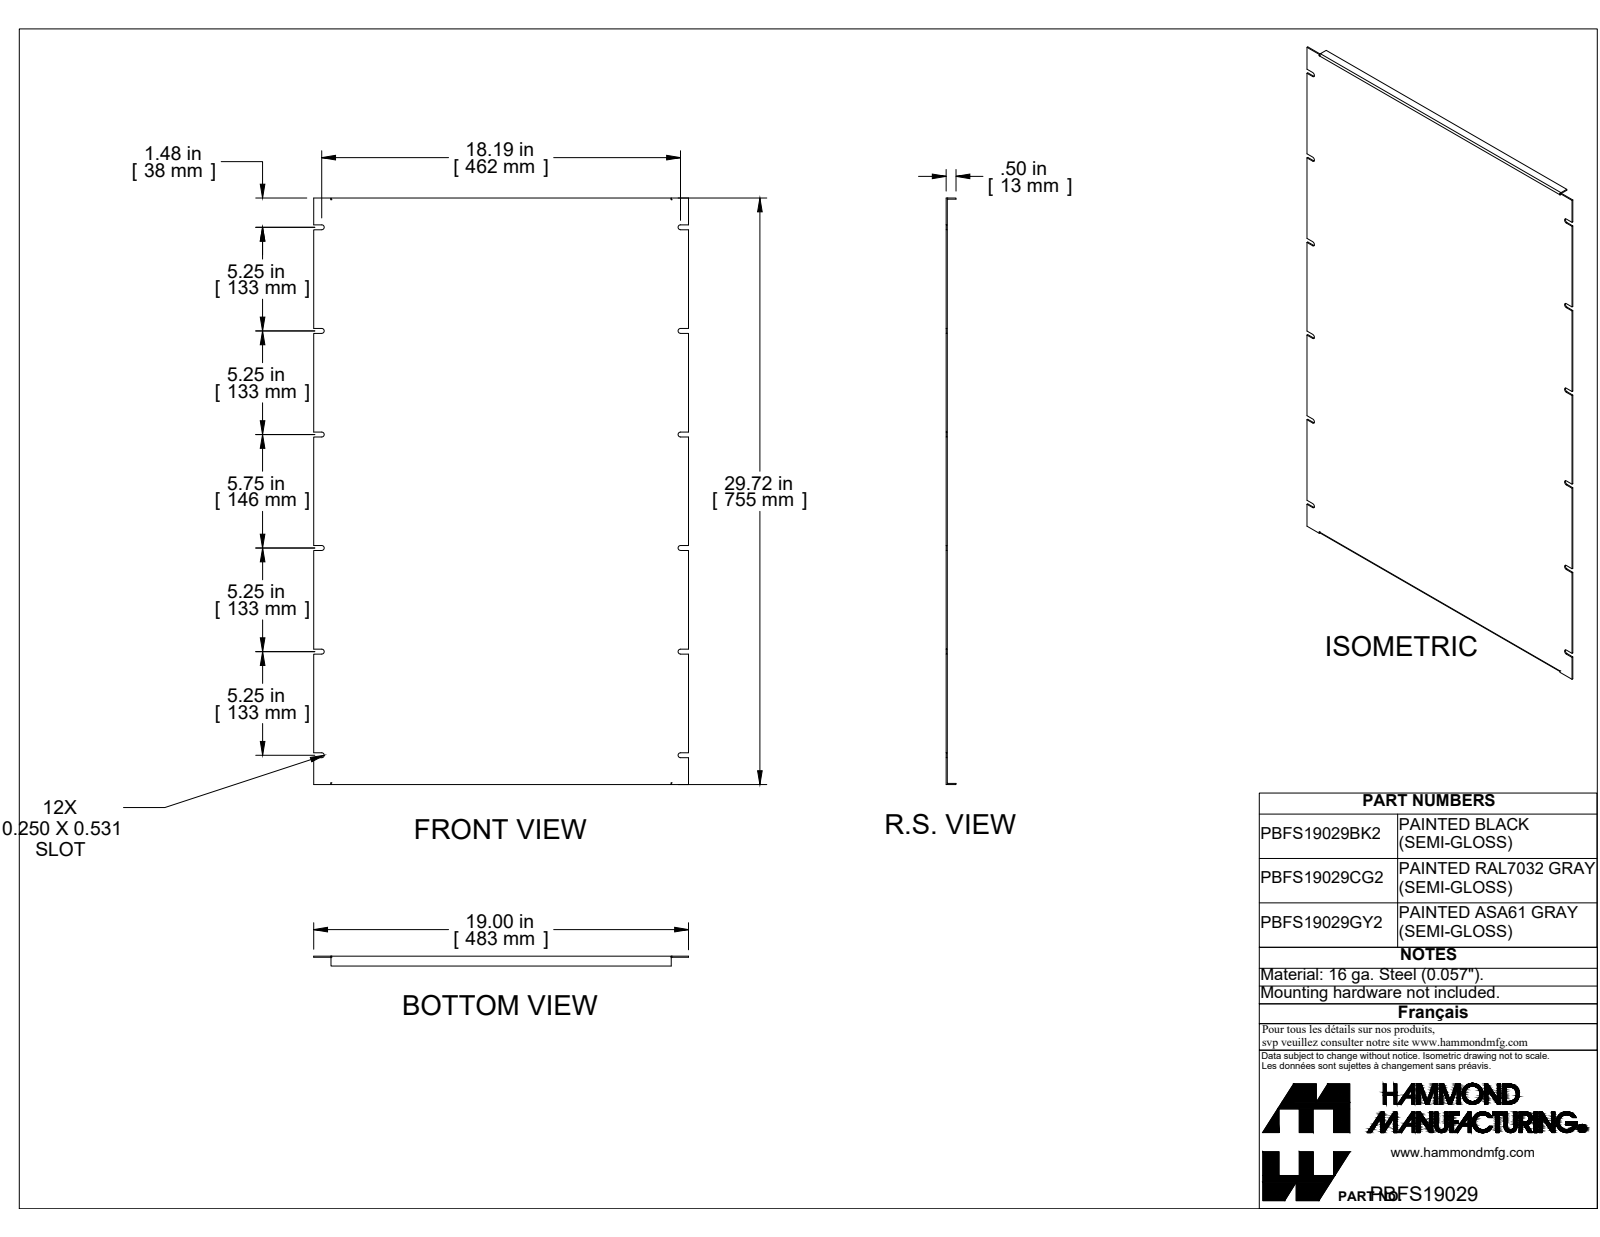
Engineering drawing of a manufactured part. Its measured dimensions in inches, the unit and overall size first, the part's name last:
Units: inches
Overall size (bounding box): 29.718 × 19 × 0.5
Partial cylindrical surfaces — rounded edges, fillets, slot ends (radius × count): R0.125 ×12, R0.029 ×2, R0.086 ×2
Main face-to-face distances: 0.057, 29.661, 29.718, 29.604, 0.5, 0.443, 19, 5.25, 0.25, 16.25
Volume: 32.92 in³ · Surface area: 1 161 in²
Bodies: 1 solid, 78 faces (62 planar, 16 cylindrical, 0 other)
Part name (STEP PRODUCT): PBFS19029
STEP written by: SolidWorks 2019 (CONFIG_CONTROL_DESIGN)
